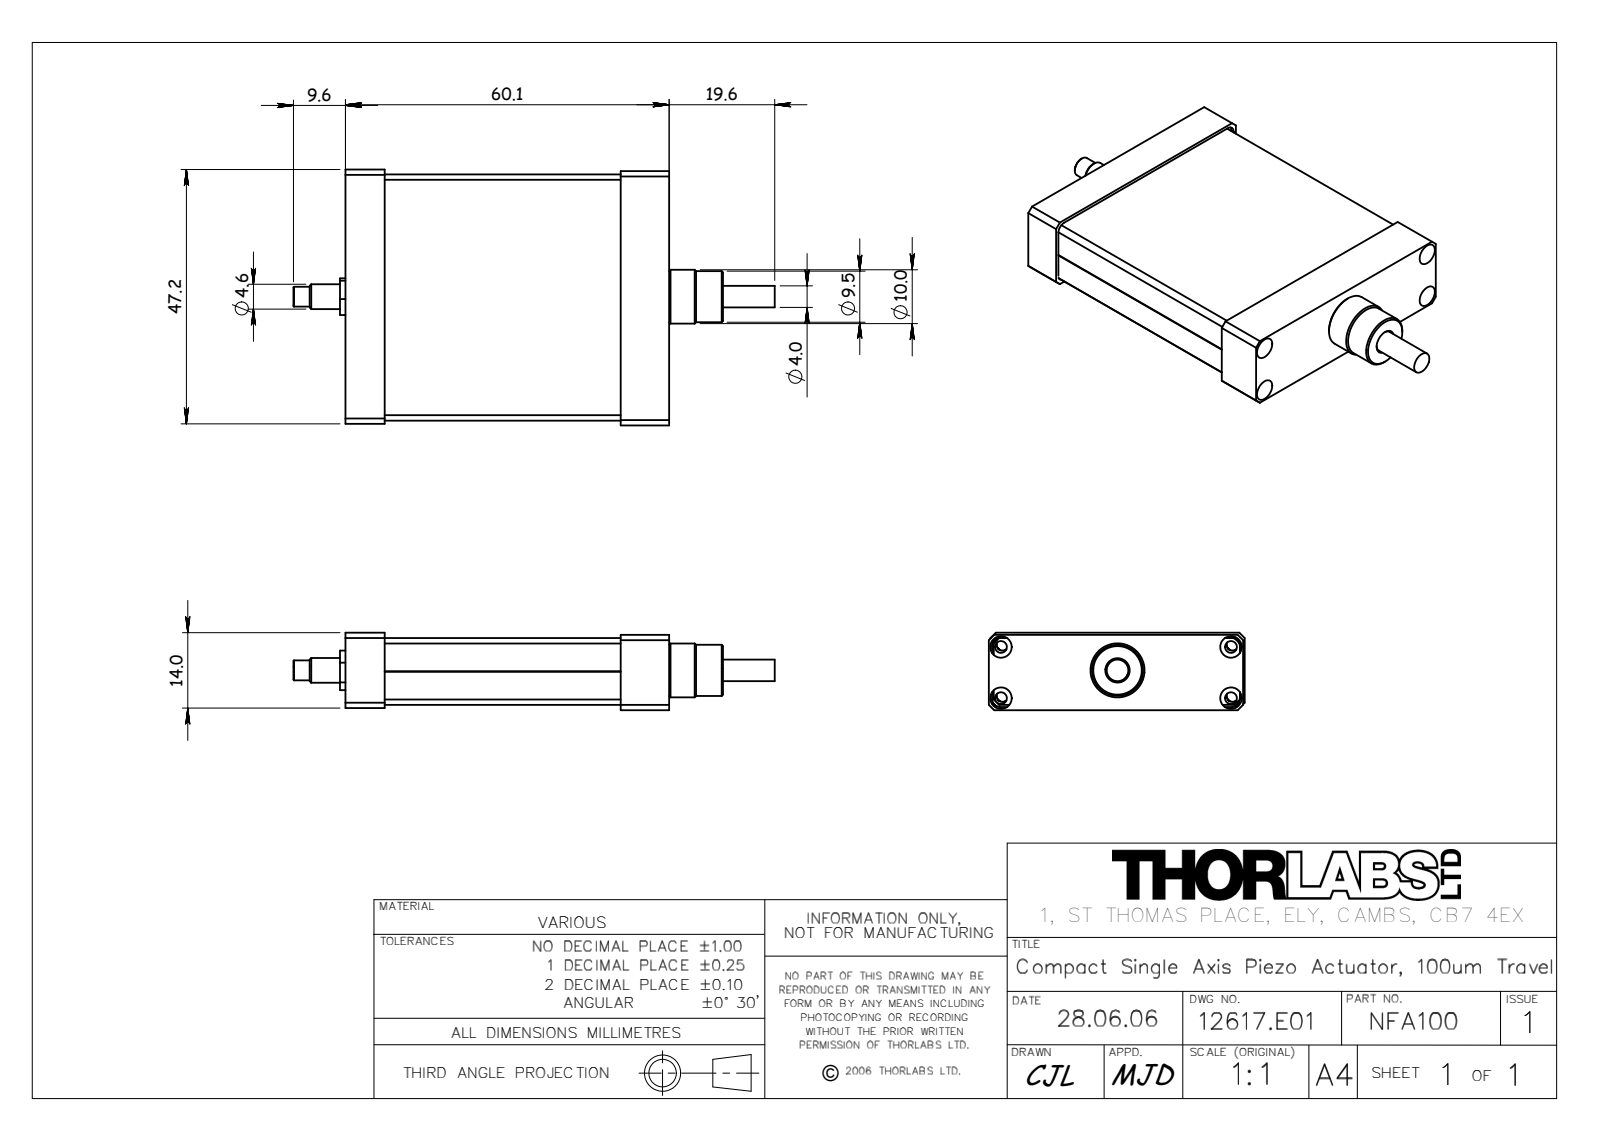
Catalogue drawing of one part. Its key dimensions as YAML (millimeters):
part_name: "12617-E0W"
step_written_by: "SolidWorks 2007 (AUTOMOTIVE_DESIGN)"
units: millimeters
bodies: {solids: 0, faces: 102, planar: 49, cylindrical: 41, other: 12}
overall_size: [89.34, 47.5, 14.4]
round_holes:
  - {diameter: 4, count: 8}
  - {diameter: 1.6, count: 2}
  - {diameter: 3, count: 1}
round_bosses_or_shafts:
  - {diameter: 10, count: 1}
  - {diameter: 9.5, count: 1}
  - {diameter: 4.6, count: 1}
  - {diameter: 4, count: 1}
  - {diameter: 3.7, count: 1}
  - {diameter: 0.5, count: 1}
partial_cylinders:
  - {radius: 1.5, count: 7}
face_to_face_distances: [12.4, 0.6, 13.4, 1, 14, 13, 0.4, 60.1, 45.7, 14.4]
hole_center_spacings: [0.5, 9.5, 21.87, 42.7, 43.74, 9.1, 9.9, 42.4]
